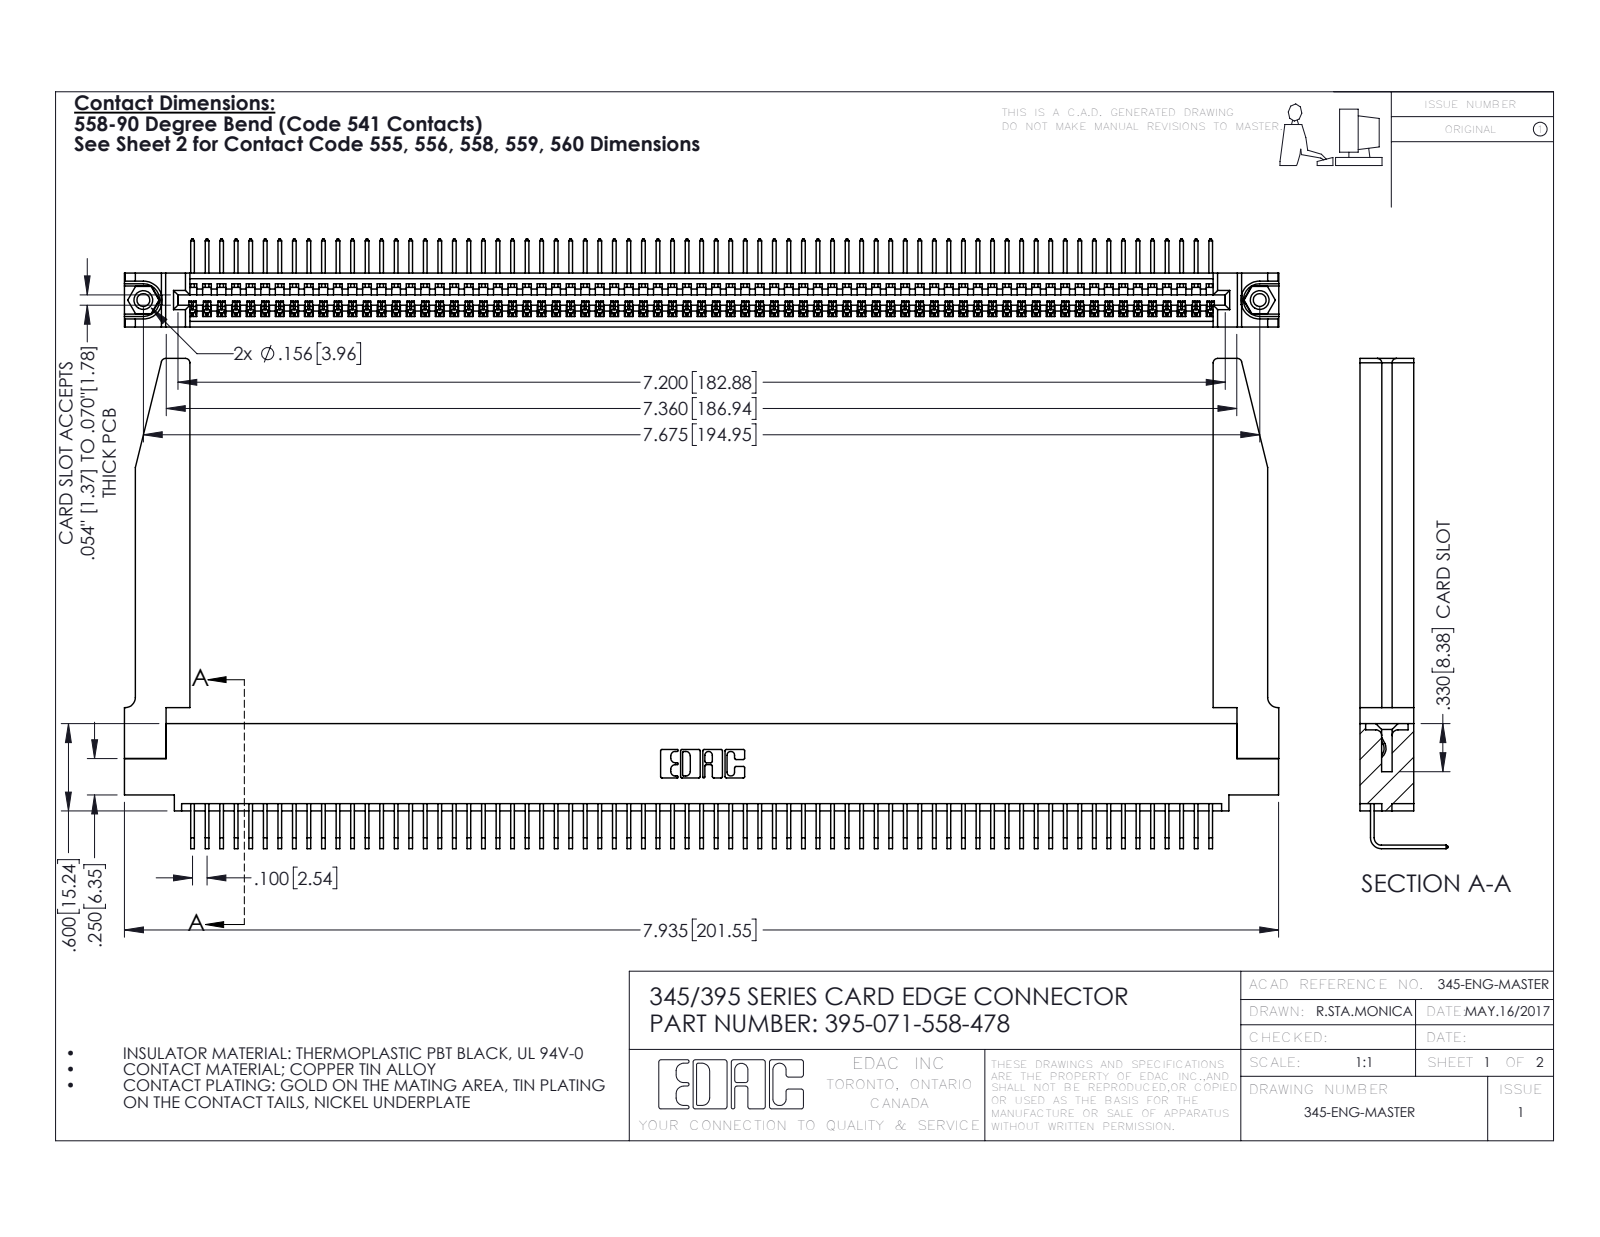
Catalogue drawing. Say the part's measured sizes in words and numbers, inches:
The part is named "345 Part_0.110 Offset - 0.156 Dia-TH; 345-250-001_345-250-001-102; 345-292-001_558 Tail - 2; 395-071-558-478 (+1 more)". Its 3-D file was written by "SolidWorks 2016 (CONFIG_CONTROL_DESIGN)". It is 76 solids with 4624 faces: 3208 planar, 1364 cylindrical and 52 other. Overall it measures 7.936 by 3.369 by 0.605 inches. Its volume is 1.667 cubic inches and its surface area 53.77 square inches. Round holes: 2 of diameter 0.089, 2 of diameter 0.125, 2 of diameter 0.156, 1 of diameter 0.064. Round bosses or shafts: 2 of diameter 0.155. Partial cylindrical surfaces (rounded edges, fillets, slot ends): 142 of radius 0.006, 22 of radius 0.01, 8 of radius 0.03, 6 of radius 0.007, 6 of radius 0.031, 3 of radius 0.026, 2 of radius 0.031, 2 of radius 0.04. The main face-to-face distances are 0.072, 0.37, 0.298, 0.098, 0.272, 0.025, 0.2, 0.225, 0.149, 0.148. The hole center spacings are 0.27, 7.439, 7.675.
